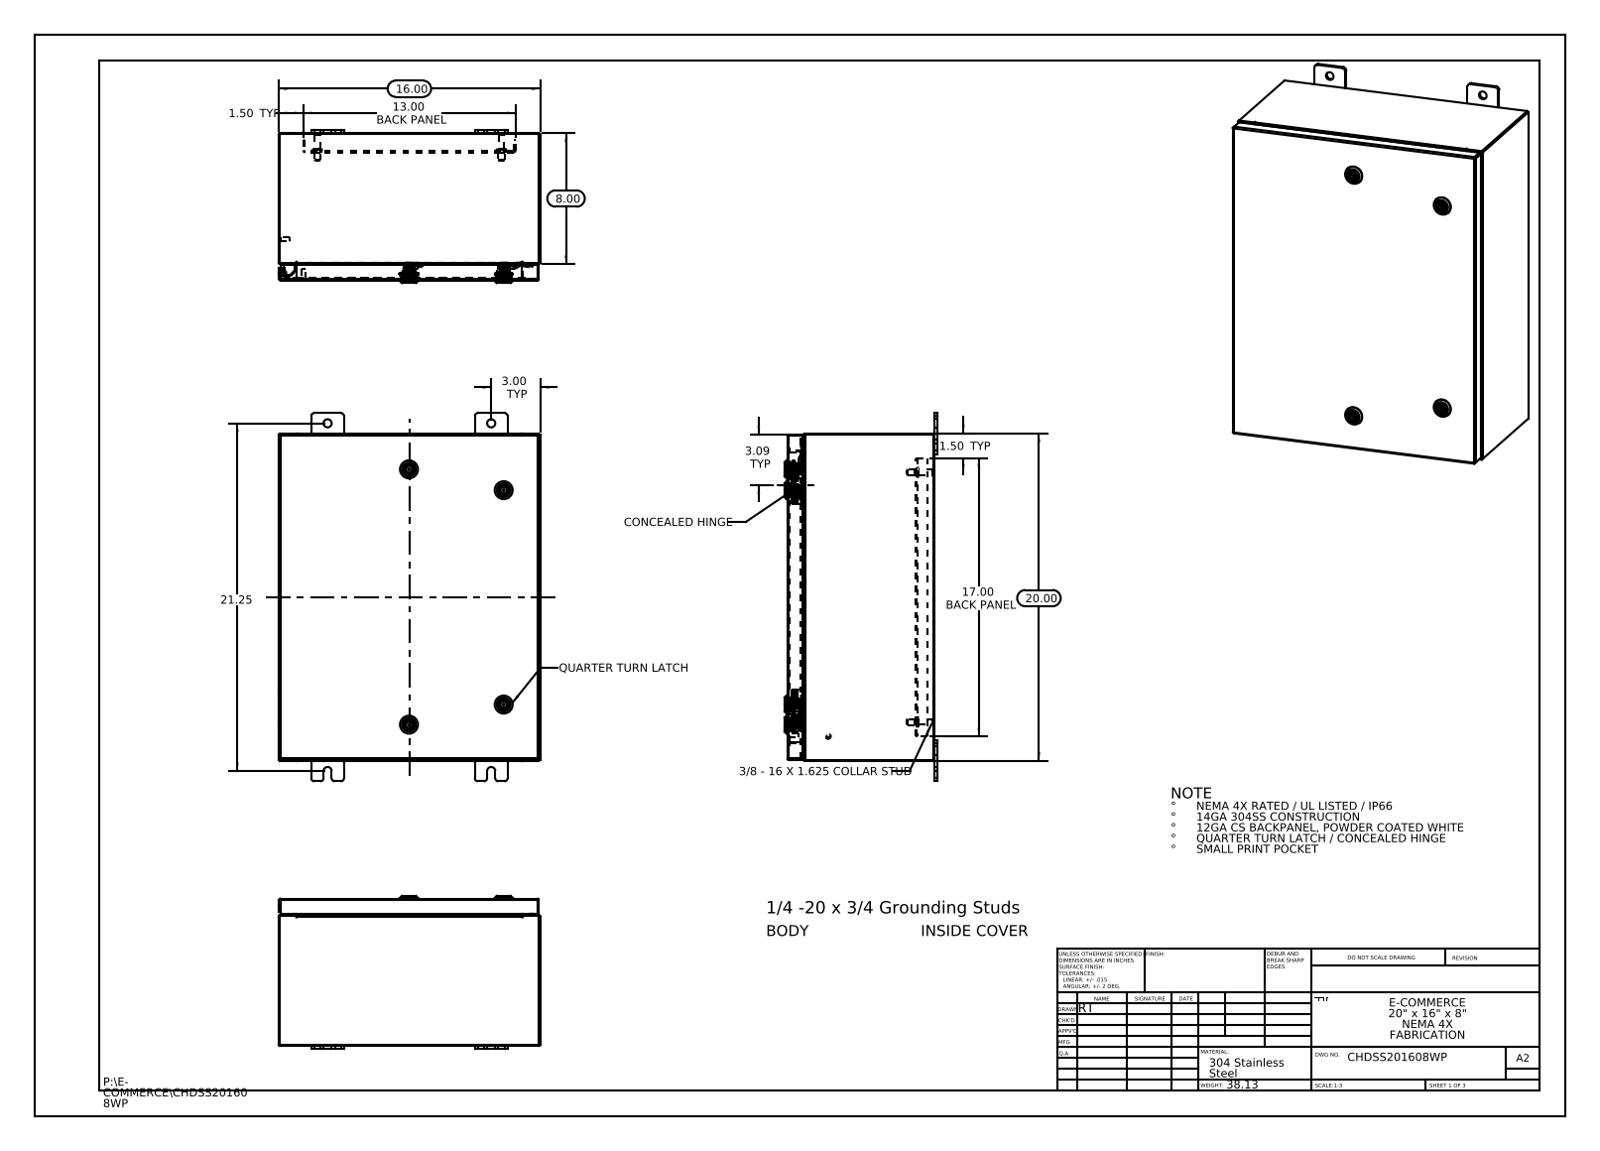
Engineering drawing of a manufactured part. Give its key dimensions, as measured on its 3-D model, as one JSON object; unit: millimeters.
{"part_name": "CHDSS201608WP Body; Screw-221320-IB-Industrilas_Screw-221320-IB-Industrilas; CHDSS201608WP Mounting Feet; CHDSS201608WP Cover (+8 more)", "step_written_by": "SolidWorks 2013 (CONFIG_CONTROL_DESIGN)", "units": "millimeters", "bodies": {"solids": 43, "faces": 3794, "planar": 1164, "cylindrical": 1186, "other": 1444}, "overall_size": [571.5, 406.4, 237.6], "volume_mm3": 2235000, "surface_area_mm2": 2210000, "round_holes": [[12.7, 8], [3.5, 4], [5, 4], [10, 4], [10.2, 4], [16, 4], [20, 4], [5.4, 2]], "round_bosses_or_shafts": [[6, 6], [28, 4], [19.8, 4], [15.9, 4], [15.9, 4], [15.5, 4], [13.5, 4], [10, 4]], "partial_cylinders_radius": [[0.2, 132], [3, 132], [0.7, 48], [4.8, 24], [0.3, 20], [2.2, 18], [0.5, 16], [5, 16]], "face_to_face_distances": [1.9, 1.9, 404.5, 228.9, 226.9, 227, 225.1, 506.1, 2.6, 25.4], "hole_center_spacings": [47.2, 77.9, 254, 285.8, 387.4, 432.1, 463.8, 481.4]}
